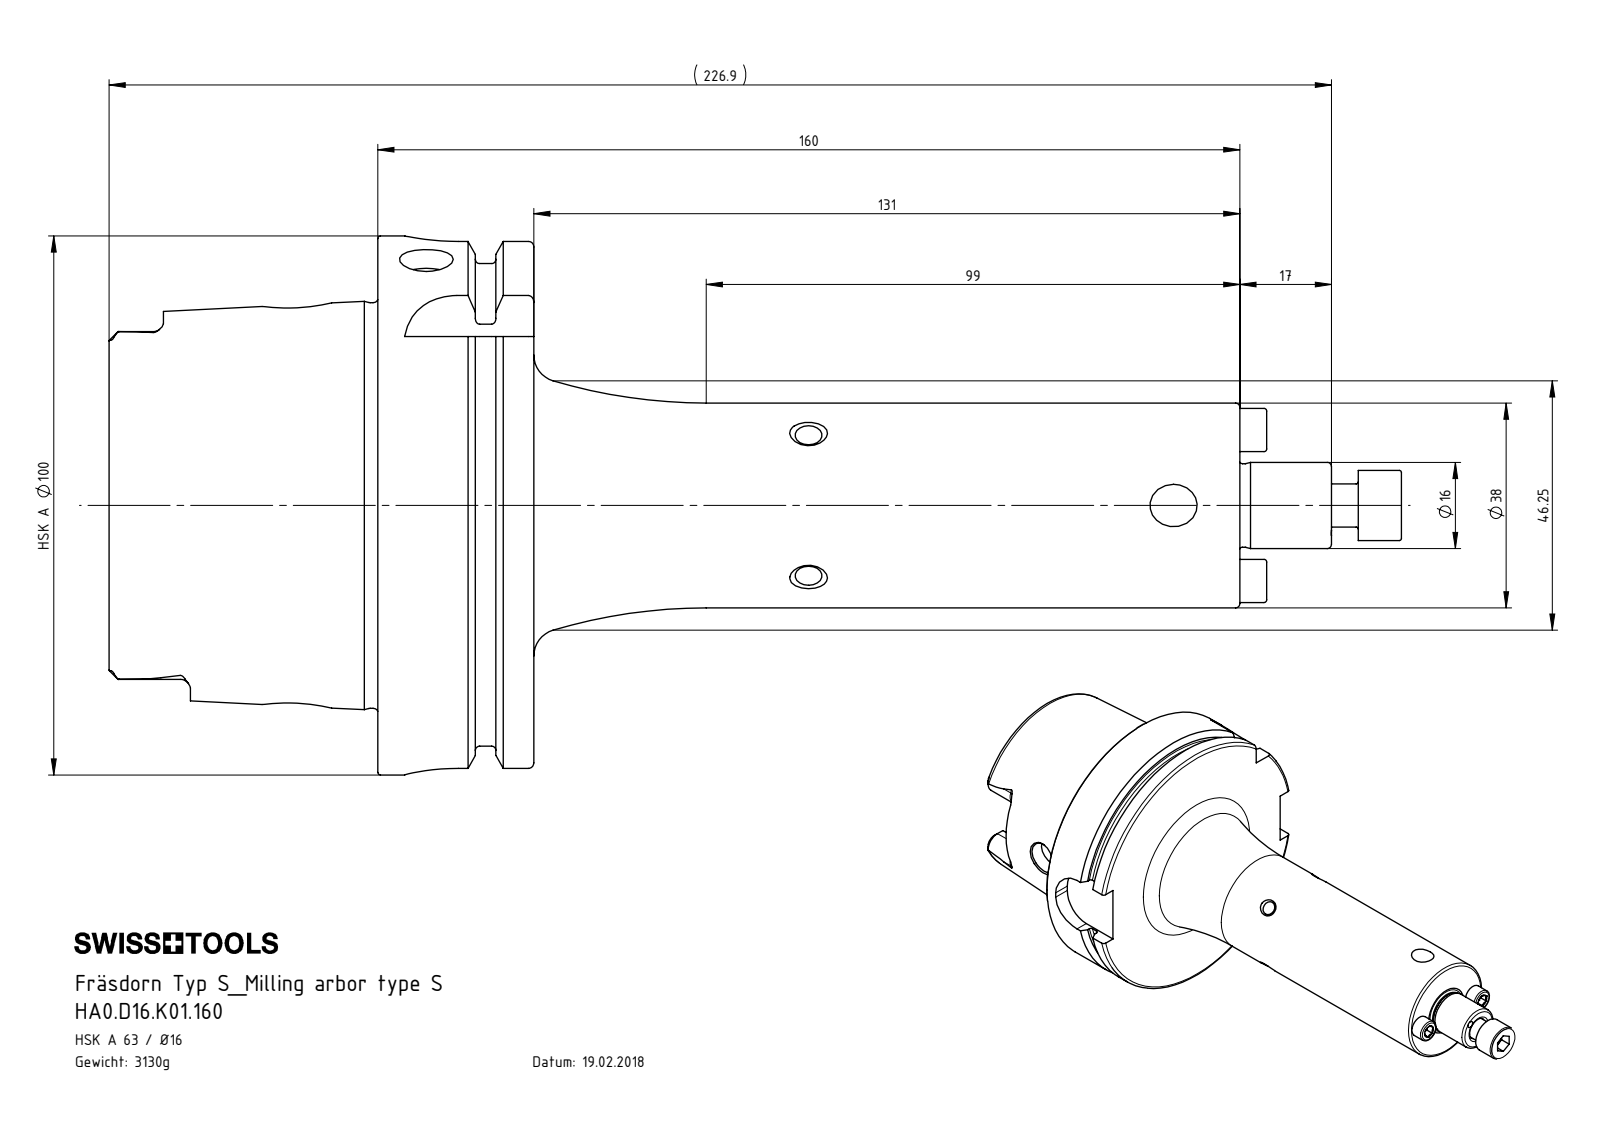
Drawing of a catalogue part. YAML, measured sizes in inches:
part_name: "HA0.D16.K01.160; D16-ER2.001.015_B; HA0-D16.K01.160_C_Fertigbearbeitung; D16-ER1.002.025_A_Default"
step_written_by: "SolidWorks 2011 (AUTOMOTIVE_DESIGN)"
units: inches
bodies: {solids: 4, faces: 374, planar: 85, cylindrical: 112, other: 177}
overall_size: [9.445, 3.937, 3.937]
volume: 24.33
surface_area: 115.6
round_holes:
  - {diameter: 0.098, count: 3}
  - {diameter: 0.394, count: 3}
  - {diameter: 0.13, count: 2}
  - {diameter: 0.197, count: 2}
  - {diameter: 0.236, count: 2}
  - {diameter: 0.472, count: 2}
  - {diameter: 0.268, count: 1}
  - {diameter: 0.335, count: 1}
  - {diameter: 0.886, count: 1}
  - {diameter: 1.024, count: 1}
  - {diameter: 2.087, count: 1}
  - {diameter: 2.48, count: 1}
round_bosses_or_shafts:
  - {diameter: 0.315, count: 3}
  - {diameter: 0.157, count: 2}
  - {diameter: 0.118, count: 2}
  - {diameter: 3.937, count: 1}
  - {diameter: 3.62, count: 1}
  - {diameter: 2.963, count: 1}
  - {diameter: 1.496, count: 1}
  - {diameter: 0.63, count: 1}
partial_cylinders:
  - {radius: 0.075, count: 6}
  - {radius: 0.192, count: 4}
  - {radius: 0.394, count: 4}
  - {radius: 0.079, count: 2}
face_to_face_distances: [1.14, 0.49, 0.65, 1.965, 2.455, 3.104, 8.264, 6.299, 5.809, 5.159]
hole_center_spacings: [0.241, 0.417, 0.551, 0.741, 0.482, 1.102, 2.915]
